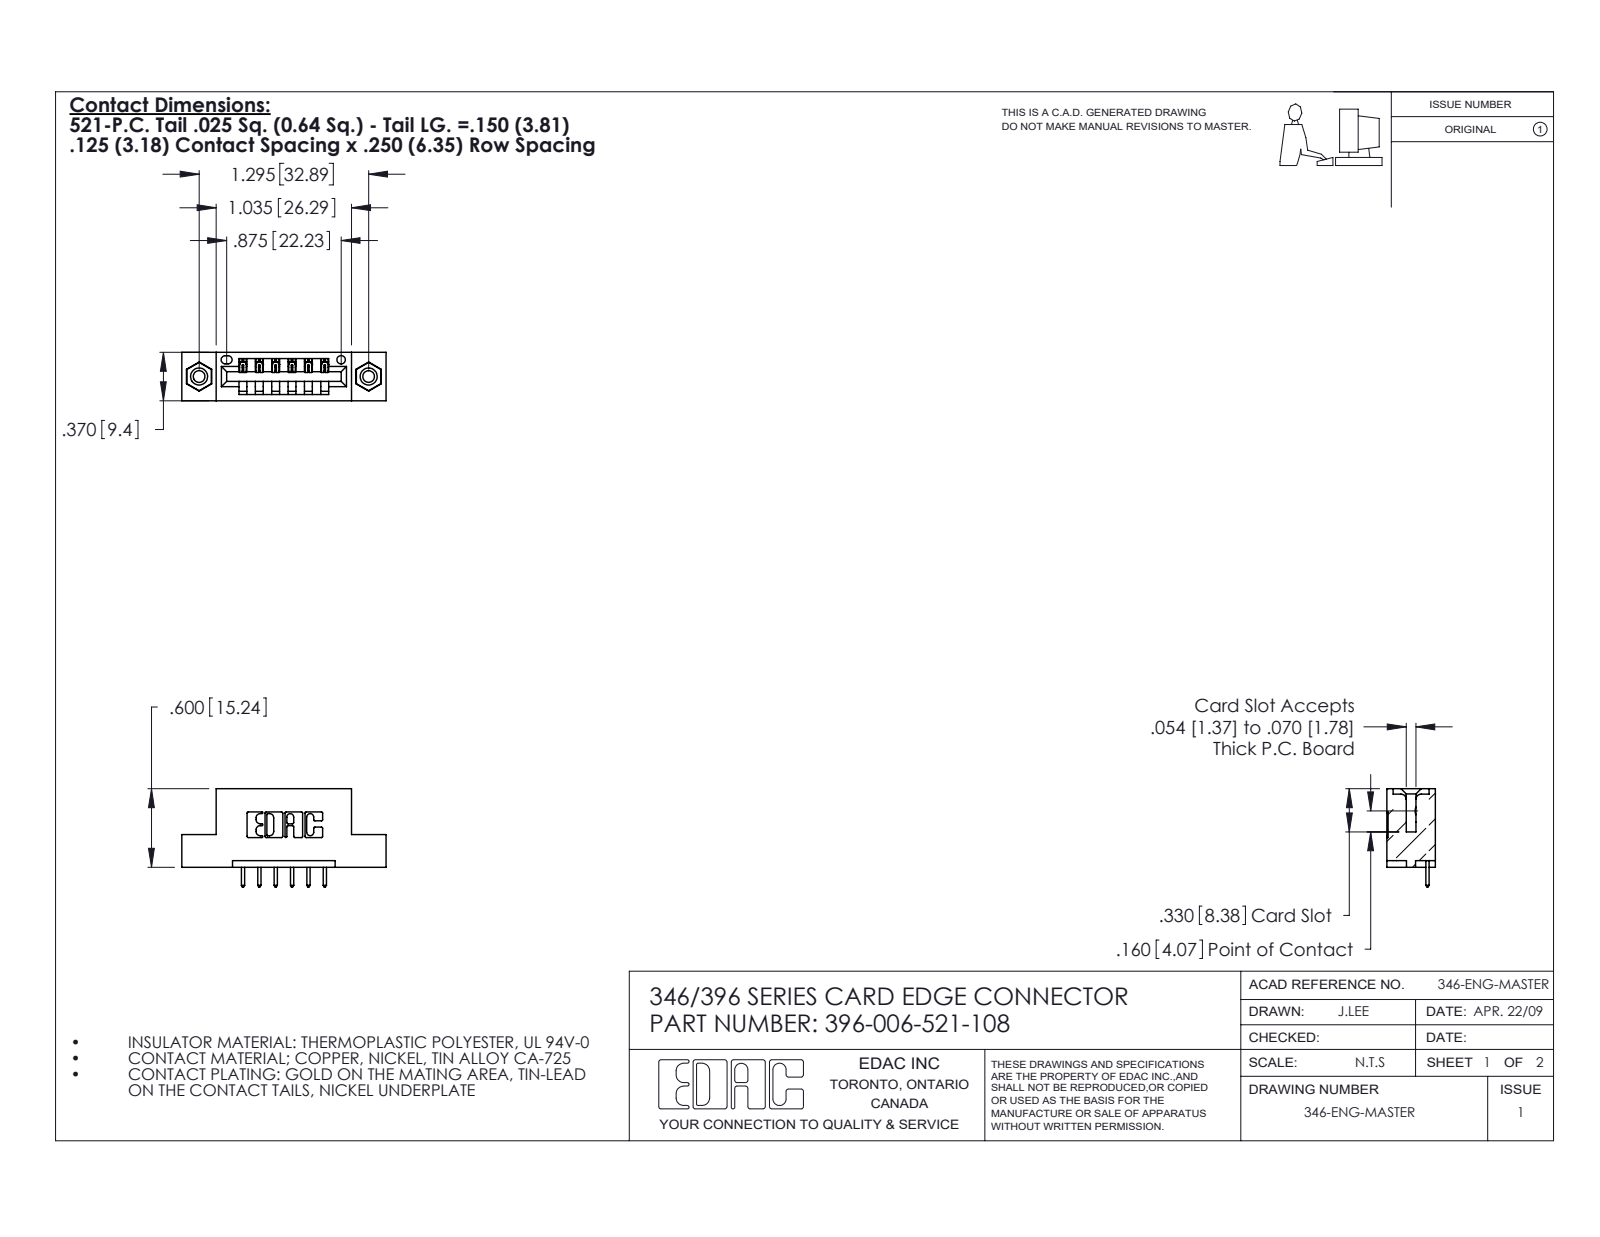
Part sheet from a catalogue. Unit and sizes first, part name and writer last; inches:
Units: inches
Overall size (bounding box): 1.56 × 0.75 × 0.37
Round holes (diameter × count): ⌀0.089 ×2, ⌀0.125 ×2, ⌀0.156 ×2, ⌀0.064 ×1
Round bosses / shafts (diameter × count): ⌀0.155 ×2
Partial cylindrical surfaces — rounded edges, fillets, slot ends (radius × count): R0.01 ×22, R0.006 ×12, R0.01 ×12, R0.007 ×6, R0.031 ×6, R0.026 ×3, R0.031 ×2, R0.04 ×2
Main face-to-face distances: 0.25, 0.37, 0.048, 0.322, 0.148, 0.222, 0.1, 0.174, 0.125, 0.125
Hole centre spacings: 0.246, 1.092, 1.295
Volume: 0.215 in³ · Surface area: 6.148 in²
Bodies: 9 solids, 530 faces (348 planar, 166 cylindrical, 16 other)
Part name (STEP PRODUCT): 345-250-001_345-250-003-102; 345-292-001_345-293-121; 396-006-521-108; 346 Part_Flush Mounting Lugs - 0.156 Dia-TI
STEP written by: SolidWorks 2020 (CONFIG_CONTROL_DESIGN)
